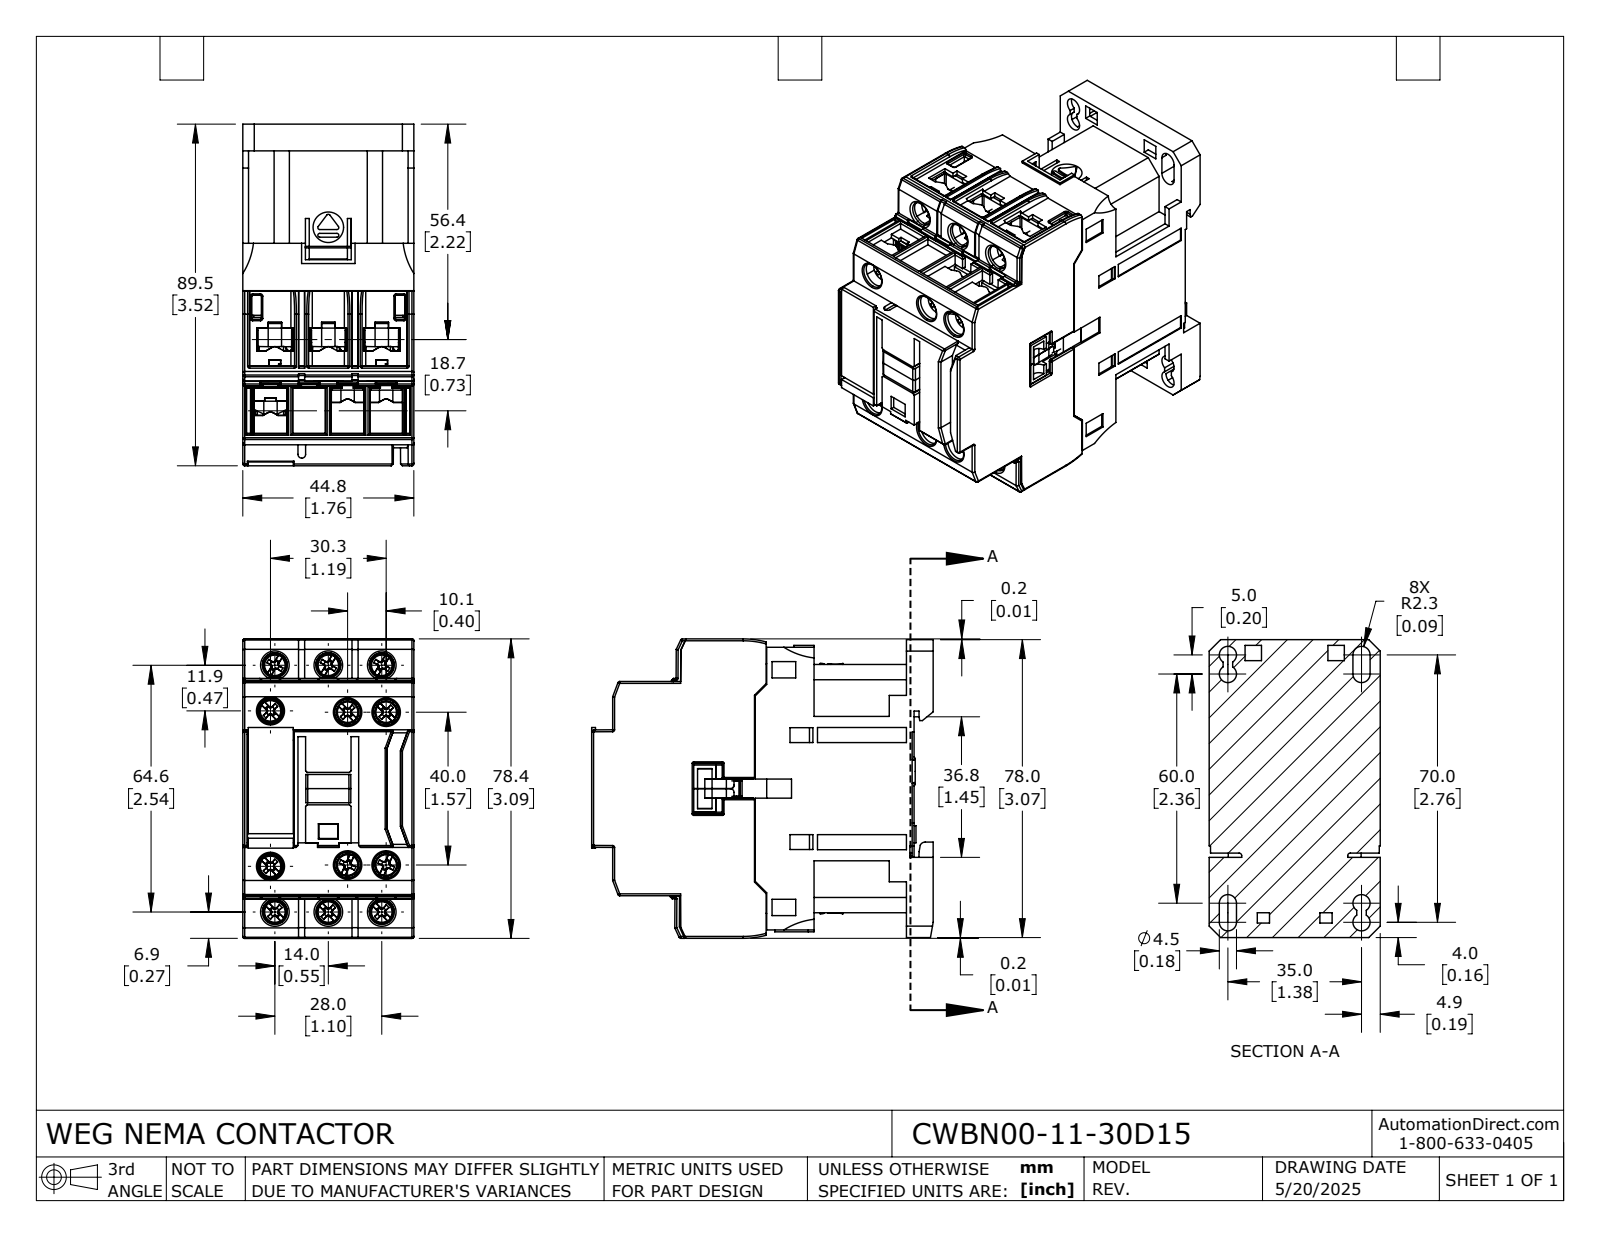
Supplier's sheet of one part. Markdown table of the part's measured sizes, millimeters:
| quantity | value |
| --- | --- |
| part name | CWBN00-11-30D15 |
| STEP written by | SolidWorks 2024 (AUTOMOTIVE_DESIGN) |
| units | millimeters |
| bodies | 44 solids, 3238 faces (2285 planar, 627 cylindrical, 326 other) |
| overall size | 89.5 × 78.4 × 44.8 |
| volume | 219 100 mm³ |
| surface area | 75 550 mm² |
| round holes (diameter × count) | 3.1 × 12, 6.5 × 6, 4.5 × 4 |
| round bosses / shafts (diameter × count) | 4.3 × 12, 3.5 × 12, 2.7 × 7, 2.7 × 5 |
| partial cylindrical surfaces (radius × count) | 0.5 × 127, 0.3 × 52, 1.8 × 24, 24.5 × 24, 54.1 × 24, 0.4 × 20, 1 × 19, 2.7 × 11 |
| main face-to-face distances | 44.8, 1.2, 43.6, 44.6, 0.6, 7, 45.1, 1.5, 0.6, 43.1 |
| hole center spacings | 14, 28, 66.1, 66.1, 64.6, 64.6, 5, 10.1 |
